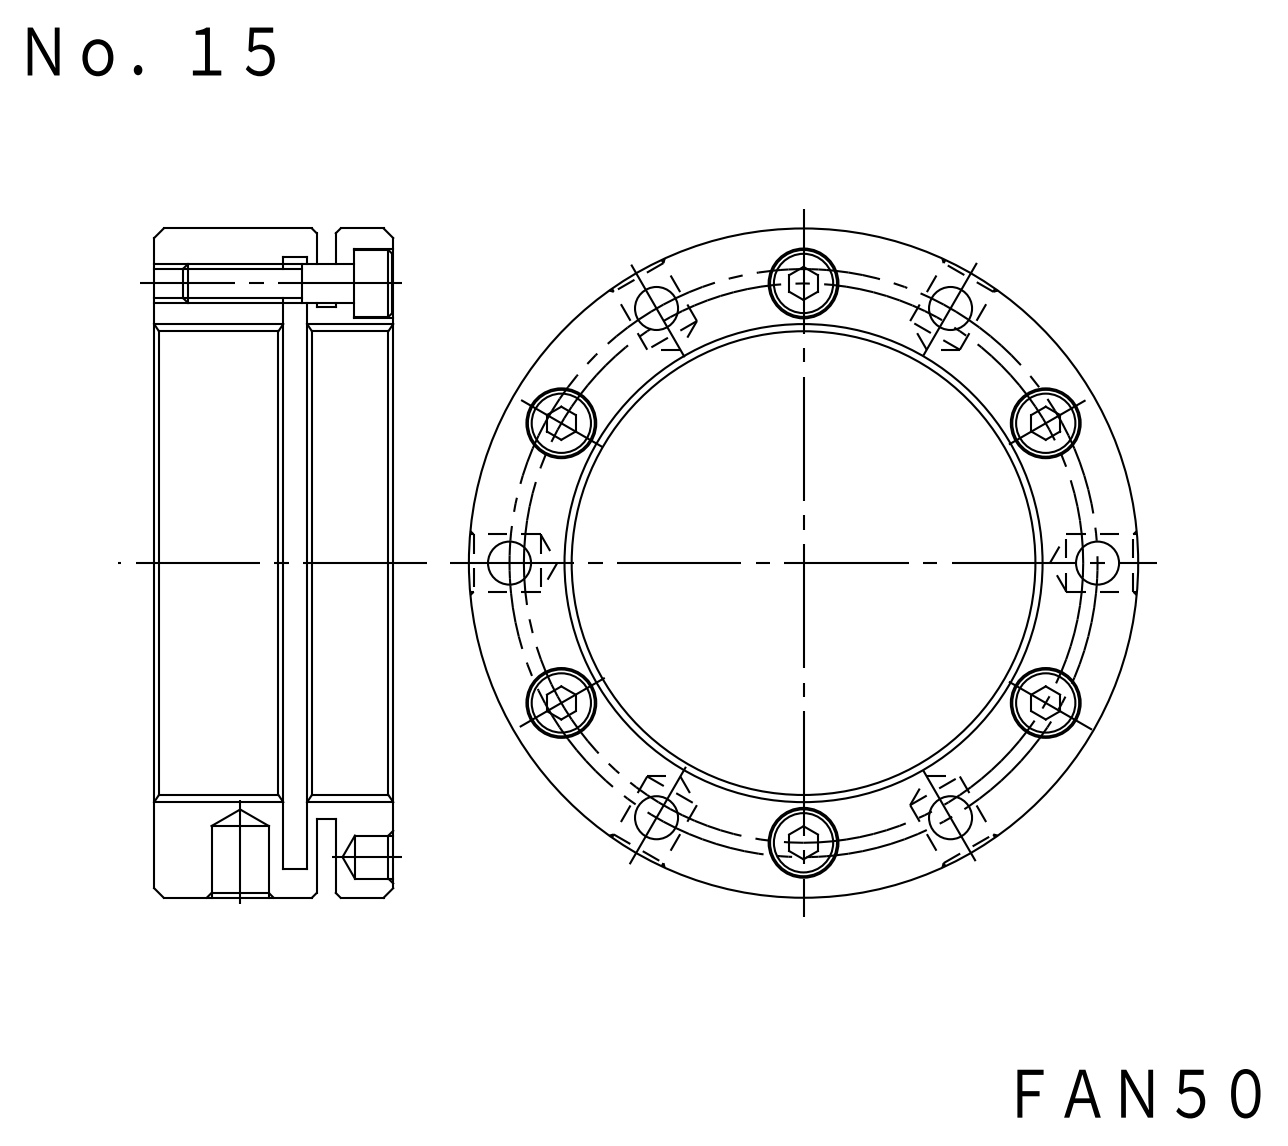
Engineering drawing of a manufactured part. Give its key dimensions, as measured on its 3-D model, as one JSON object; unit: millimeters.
{"part_name": "FKD FAN50; M4X18_default", "step_written_by": "SolidWorks 2012 (CONFIG_CONTROL_DESIGN)", "units": "millimeters", "bodies": {"solids": 7, "faces": 204, "planar": 72, "cylindrical": 108, "other": 24}, "overall_size": [70, 70, 25], "volume_mm3": 39311, "surface_area_mm2": 23662, "round_holes": [[3.24, 6], [4.3, 6], [4.5, 6], [7.3, 6], [6, 3], [50, 1], [65, 1]], "round_bosses_or_shafts": [[7, 6], [4, 6], [70, 1], [55, 1]], "face_to_face_distances": [6, 25, 4, 2, 19, 17, 8, 13, 12, 15.5], "hole_center_spacings": [15.74, 30, 58.68, 30.75, 42.96, 51.96, 53.26, 60]}
